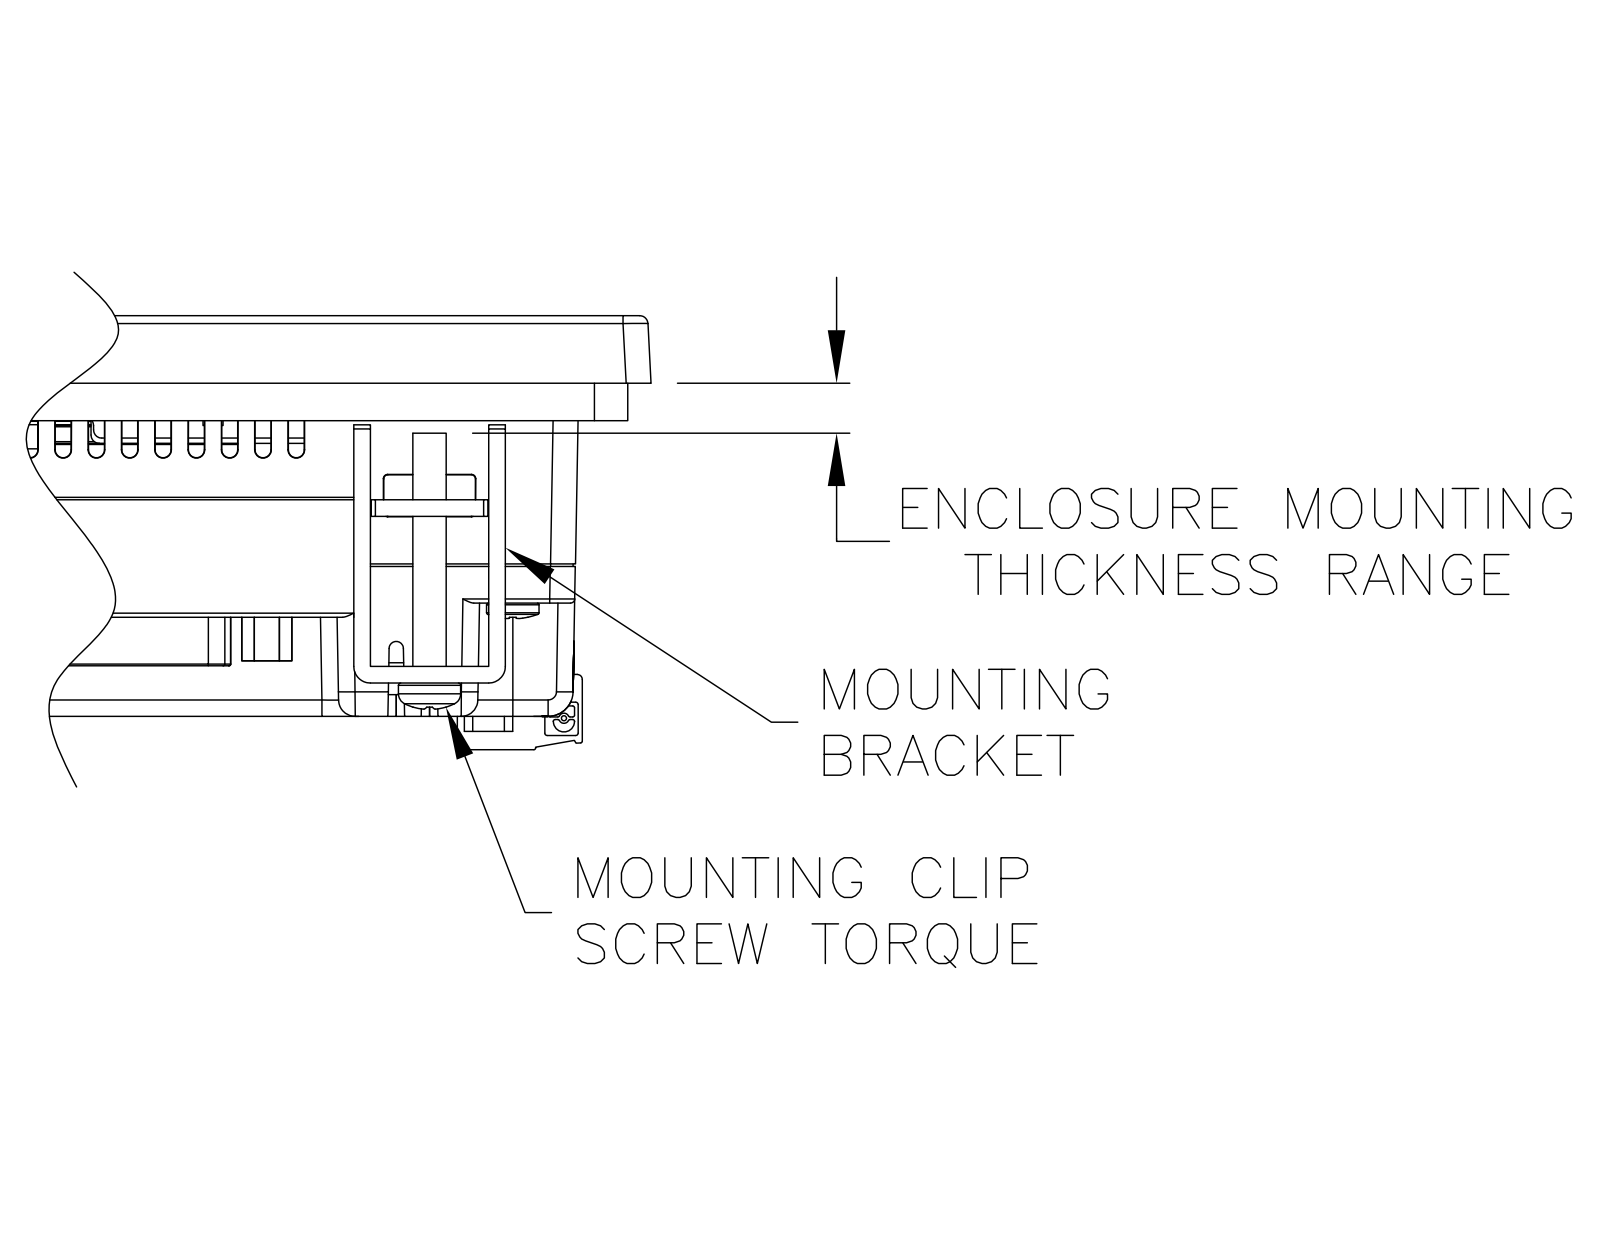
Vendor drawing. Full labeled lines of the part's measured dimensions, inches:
Part name (STEP PRODUCT): EA9-T6CL
STEP written by: SolidWorks 2014 (AUTOMOTIVE_DESIGN)
Units: inches
Bodies: 6 solids, 1342 faces (719 planar, 587 cylindrical, 36 other)
Overall size (bounding box): 8.08 × 6.13 × 1.925
Volume: 16.73 in³ · Surface area: 309.9 in²
Round holes (diameter × count): ⌀0.045 ×14, ⌀0.07 ×2, ⌀0.08 ×2, ⌀0.44 ×2, ⌀0.045 ×1
Round bosses / shafts (diameter × count): ⌀0.04 ×5
Partial cylindrical surfaces — rounded edges, fillets, slot ends (radius × count): R0.04 ×105, R0.042 ×97, R0.031 ×44, R0.045 ×41, R0.063 ×20, R0.125 ×13, R0.062 ×9, R0.025 ×8
Main face-to-face distances: 0.1, 1.824, 0.35, 1.474, 5.32, 1.924, 0.25, 1.724, 0.45, 1.574
Hole centre spacings: 0.115, 0.15, 0.152, 0.224, 0.229, 0.343, 0.458, 0.229
